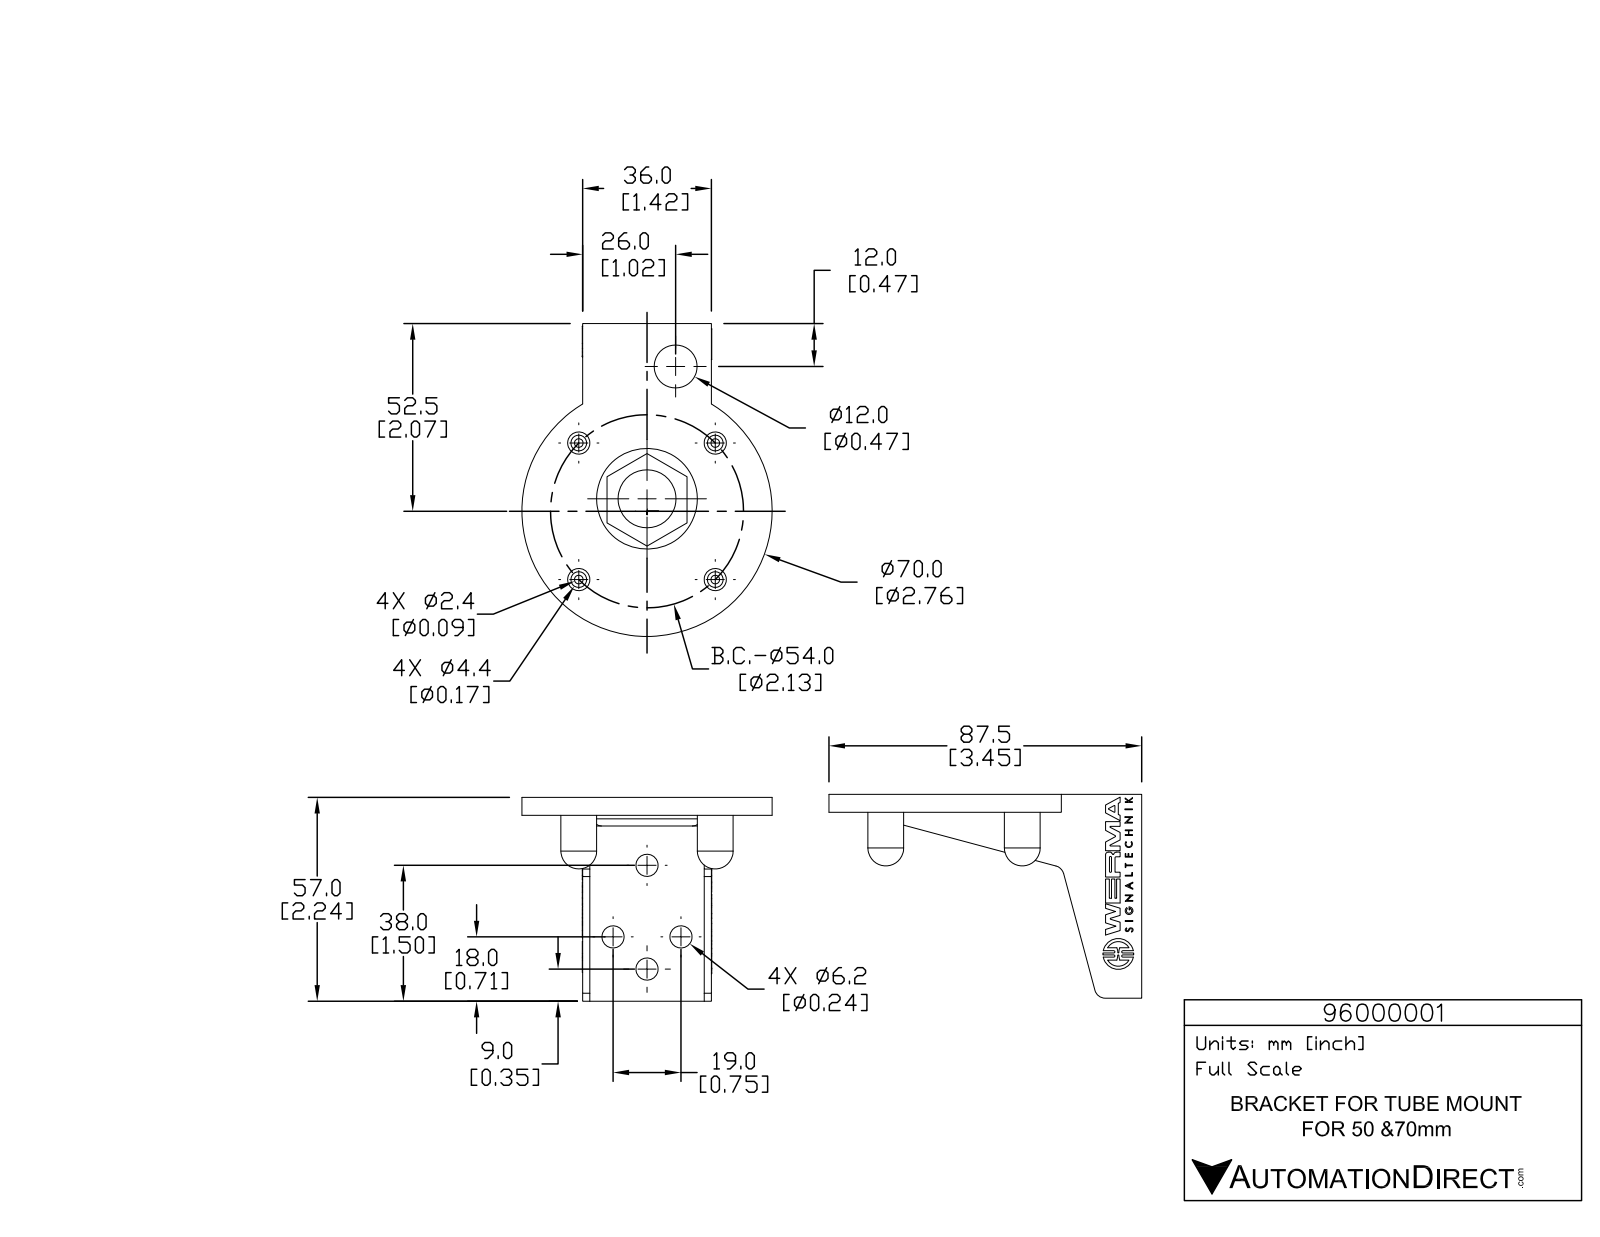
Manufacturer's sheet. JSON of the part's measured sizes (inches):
{"part_name": "96000001", "step_written_by": "SolidWorks 2015 (AUTOMOTIVE_DESIGN)", "units": "inches", "bodies": {"solids": 1, "faces": 685, "planar": 482, "cylindrical": 179, "other": 24}, "overall_size": [3.445, 2.756, 2.244], "volume_in3": 1.531, "surface_area_in2": 37.02, "round_holes": [[0.244, 8], [0.173, 4], [0.059, 2], [0.315, 1], [0.472, 1], [0.638, 1], [1.109, 1], [2.677, 1]], "round_bosses_or_shafts": [[0.394, 4], [0.472, 2], [0.339, 2], [0.084, 2], [2.756, 1]], "partial_cylinders_radius": [[0.005, 6], [0.005, 4], [0.012, 4], [0.012, 4], [0.012, 4], [0.196, 4], [0.005, 2], [0.005, 2]], "face_to_face_distances": [0.079, 1.339, 1.417, 1.26, 0.157, 0.236, 0.118, 0.315, 0.039, 0.197], "hole_center_spacings": [1.063, 1.503, 0.515, 0.872, 0.97, 1.165, 2.126, 0.138]}
